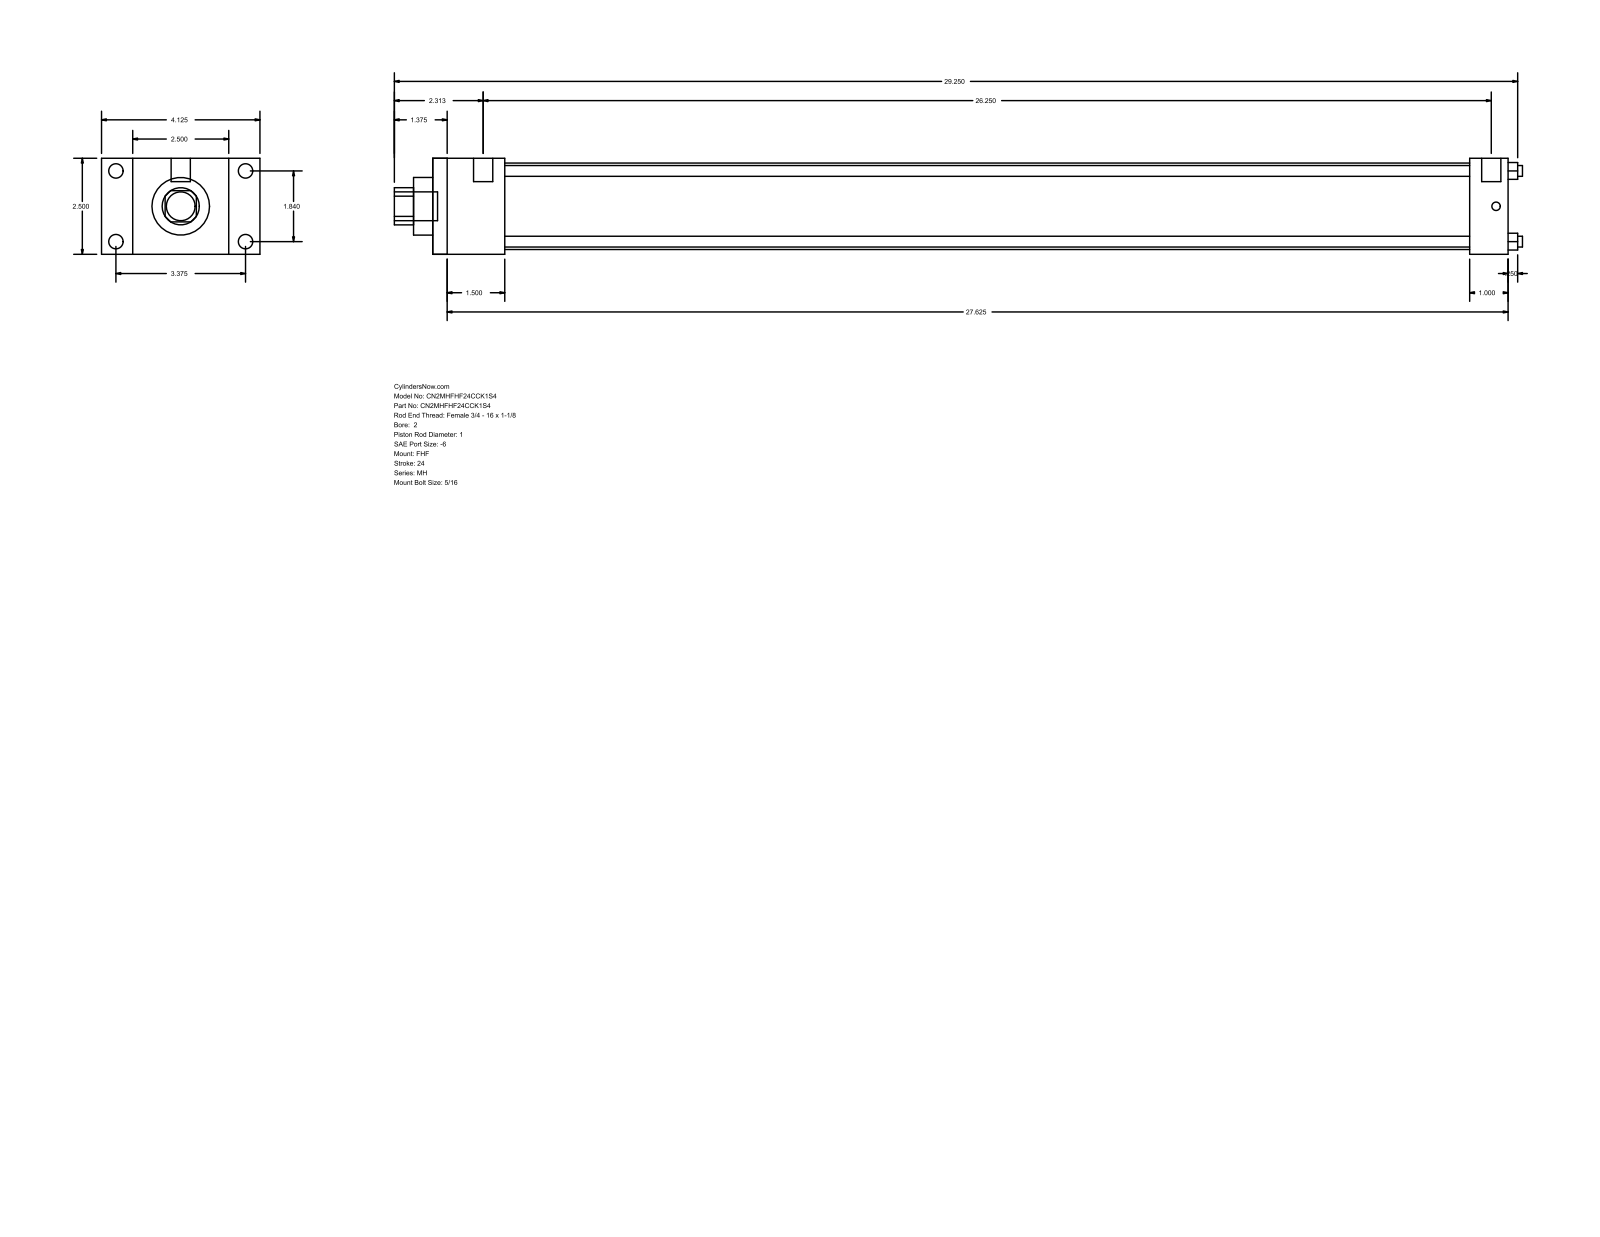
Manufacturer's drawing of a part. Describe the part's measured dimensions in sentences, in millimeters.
The part is named "MH_FHF__0200_1". Its 3-D file was written by "GSSL Pune (CONFIG_CONTROL_DESIGN)". It is 0 solids with 88 faces: 60 planar, 28 cylindrical and 0 other. Overall it measures 746.12 by 104.78 by 63.5 millimeters. Round holes: 4 of diameter 7.14, 1 of diameter 25.4, 1 of diameter 38.1, 1 of diameter 57.15. Round bosses or shafts: 4 of diameter 9.53, 4 of diameter 5.56, 2 of diameter 12.7, 1 of diameter 19.05. Partial cylindrical surfaces (rounded edges, fillets, slot ends): 1 of radius 12.29. The main face-to-face distances are 63.5, 711.2, 47.63, 663.57, 20.64, 84.14, 104.78, 25.4, 685.8, 638.17. The hole center spacings are 33.05, 46.74, 66.1.
